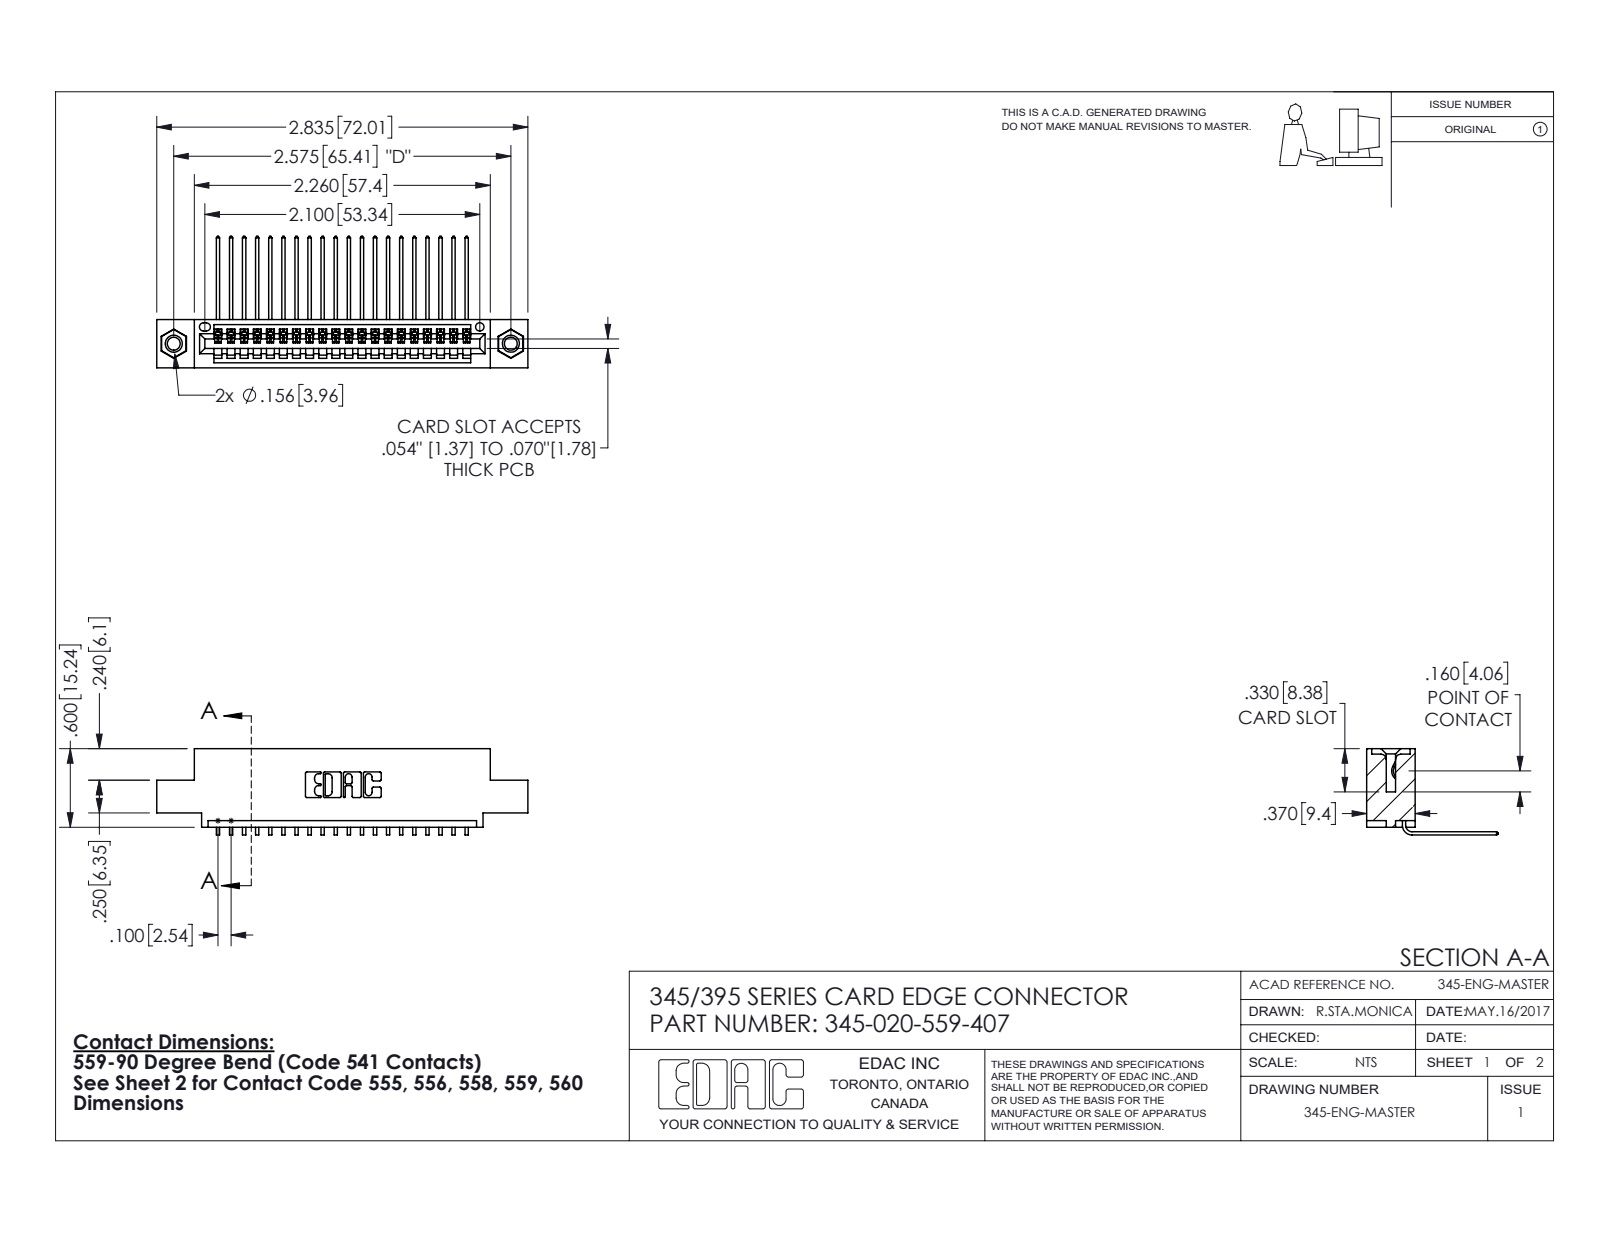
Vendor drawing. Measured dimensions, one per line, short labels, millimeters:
name: 345-250-001_345-250-005-103; 345 Part_0.110 Offset - 0.156 Dia-TI; 345-020-559-407; 345-292-001_558 559 Tail - 1
written by: SolidWorks 2016 (CONFIG_CONTROL_DESIGN)
unit: mm
bodies: 23 solids, 1390 faces (956 planar, 418 cylindrical, 16 other)
size: 72 × 25.5 × 16.7
volume: 6 640 mm³; area: 9 032 mm²
holes: 2× ⌀2.5, 2× ⌀3.2, 2× ⌀4, 1× ⌀1.6
bosses: 2× ⌀3.9
rounds: 40× R0.2, 22× R0.3, 6× R0.2, 6× R0.8, 3× R0.7, 2× R0.8, 2× R1, 1× R0.4
face distances: 1.8, 7.6, 9.4, 5.1, 2.5, 6.9, 0.6, 5.7, 3.8, 15.2
hole spacings: 6.9, 59.5, 65.4
